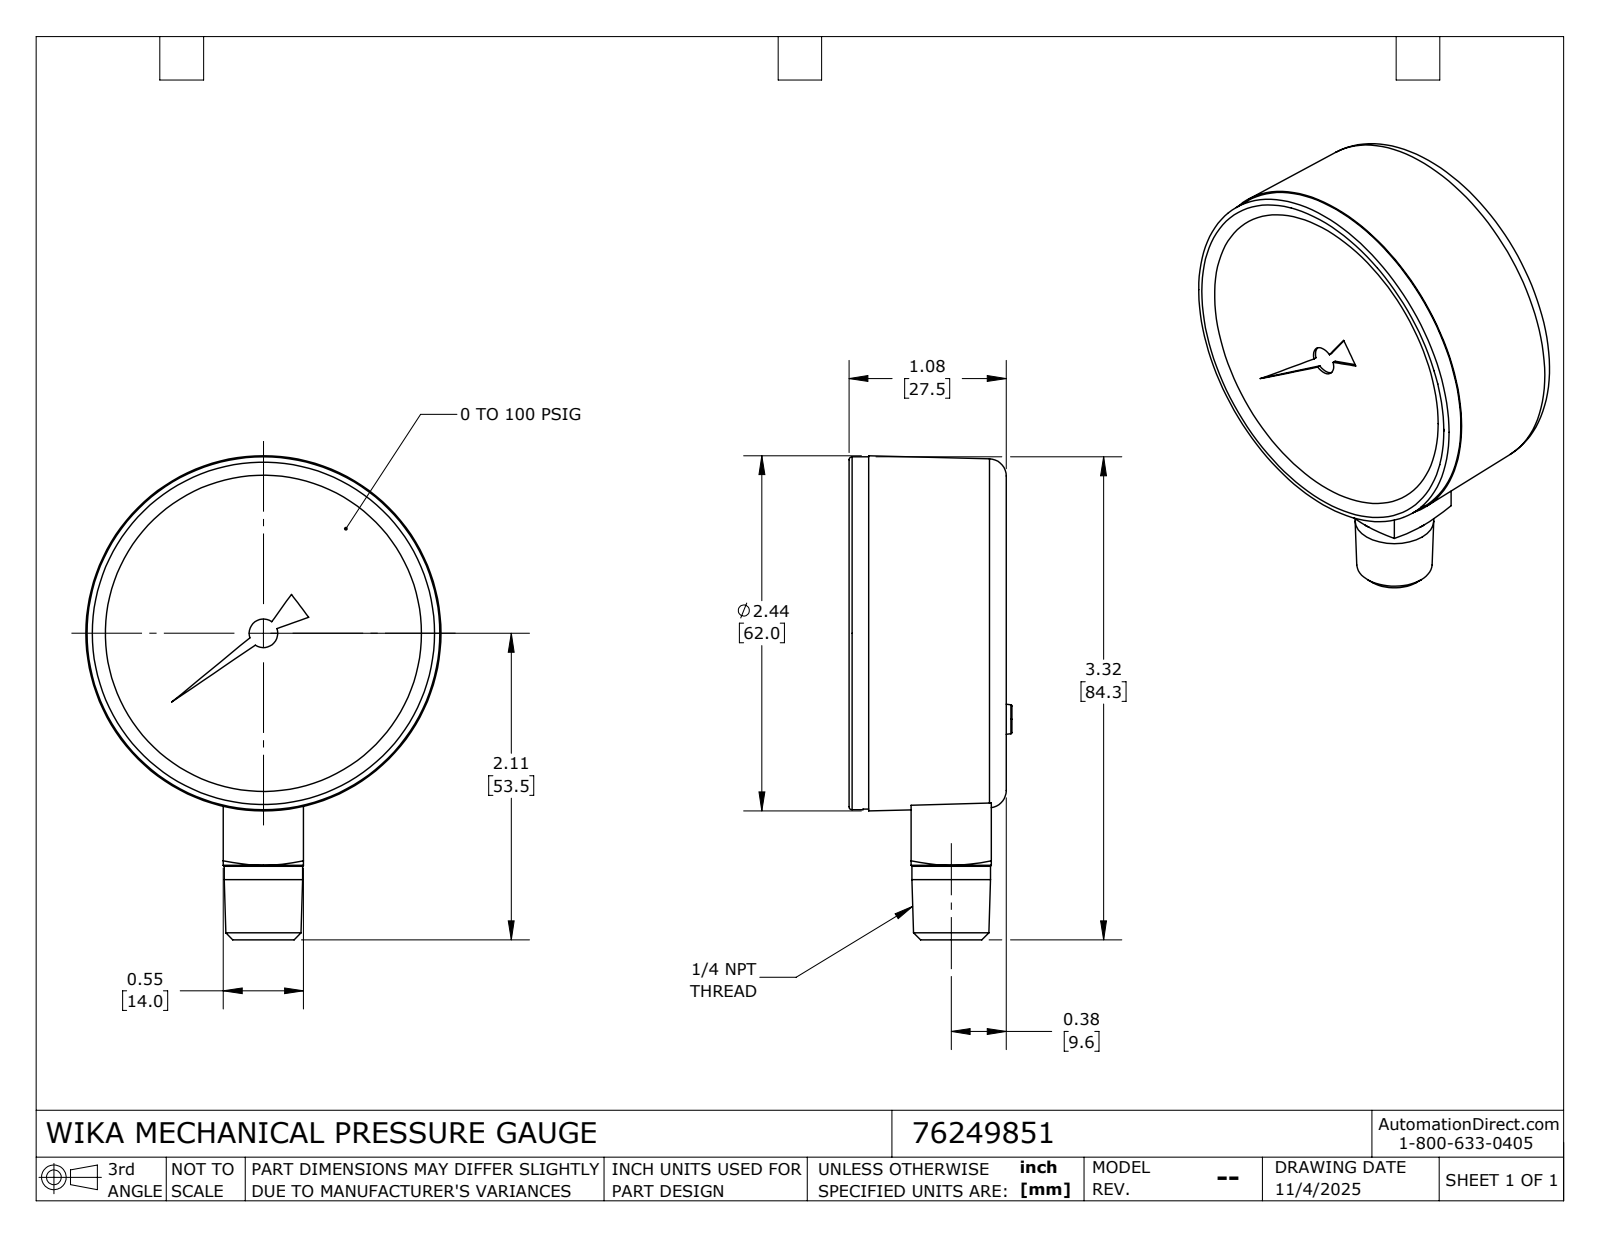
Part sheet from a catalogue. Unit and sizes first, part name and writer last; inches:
Units: inches
Overall size (bounding box): 3.327 × 2.441 × 1.12
Round holes (diameter × count): ⌀0.11 ×2, ⌀0.256 ×2, ⌀0.118 ×1, ⌀0.197 ×1, ⌀2.165 ×1
Round bosses / shafts (diameter × count): ⌀0.216 ×2, ⌀2.425 ×1, ⌀0.54 ×1
Partial cylindrical surfaces — rounded edges, fillets, slot ends (radius × count): R0.01 ×12, R0.016 ×12, R1.153 ×1
Main face-to-face distances: 0.945, 0.551, 0.039, 0.102, 0.843, 0.654, 0.291, 0.063, 0.614, 0.906
Hole centre spacings: 0.617, 0.354
Volume: 4.9 in³ · Surface area: 26.9 in²
Bodies: 3 solids, 145 faces (59 planar, 48 cylindrical, 38 other)
Part name (STEP PRODUCT): 76249851
STEP written by: SolidWorks 2024 (CONFIG_CONTROL_DESIGN)
